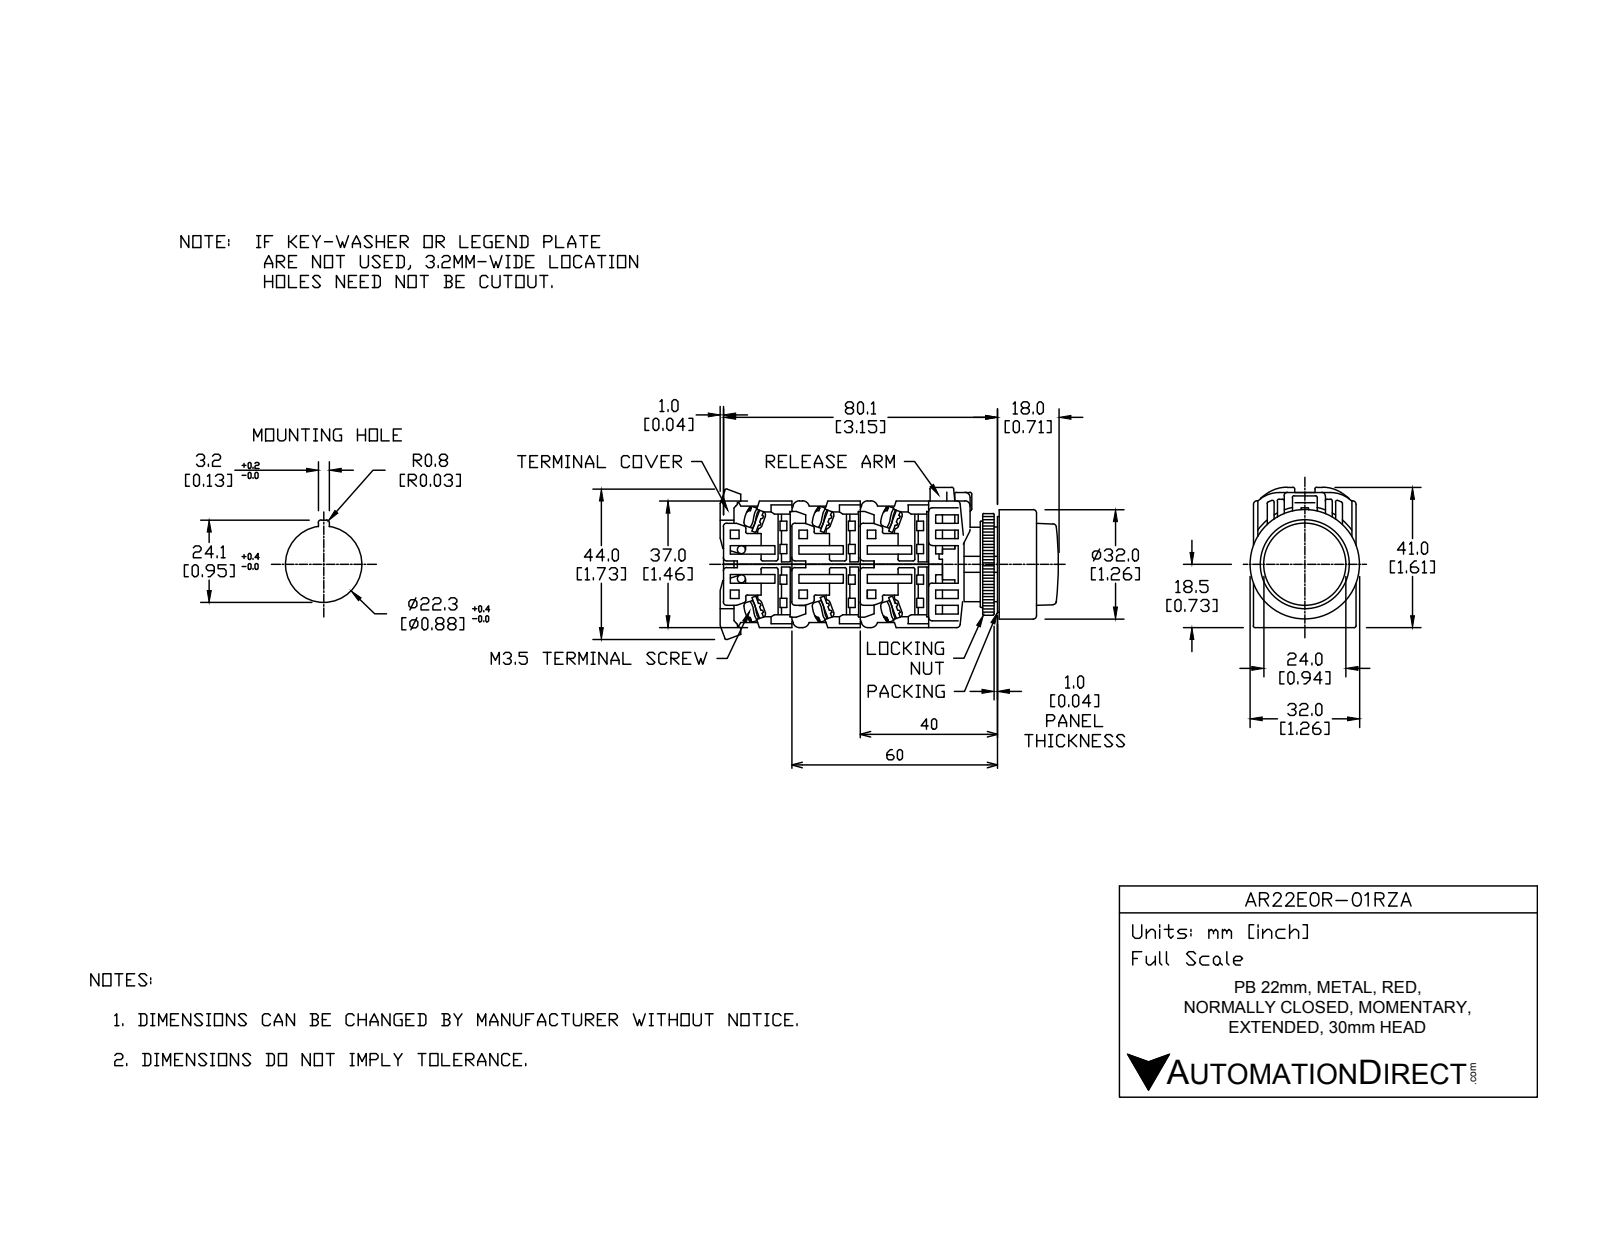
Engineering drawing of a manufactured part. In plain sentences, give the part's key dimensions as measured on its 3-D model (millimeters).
The part is named "AR22E0R-01RZA". Its 3-D file was written by "SolidWorks 2017 (AUTOMOTIVE_DESIGN)". It is 12 solids with 297 faces: 201 planar, 74 cylindrical and 22 other. Overall it measures 59.75 by 41 by 32 millimeters. Its volume is 30 443 cubic millimeters and its surface area 19 885 square millimeters. Round holes: 1 of diameter 21.8, 1 of diameter 22, 1 of diameter 25, 1 of diameter 31. Round bosses or shafts: 2 of diameter 5, 1 of diameter 32, 1 of diameter 30.5, 1 of diameter 29.8, 1 of diameter 24, 1 of diameter 23.8, 1 of diameter 21.75, 1 of diameter 17. Partial cylindrical surfaces (rounded edges, fillets, slot ends): 23 of radius 0.5, 4 of radius 1.75, 4 of radius 5, 2 of radius 4, 1 of radius 16.59, 1 of radius 17.59. The main face-to-face distances are 1, 28.5, 18, 3, 2, 29, 30, 10.5, 8, 20.5.
